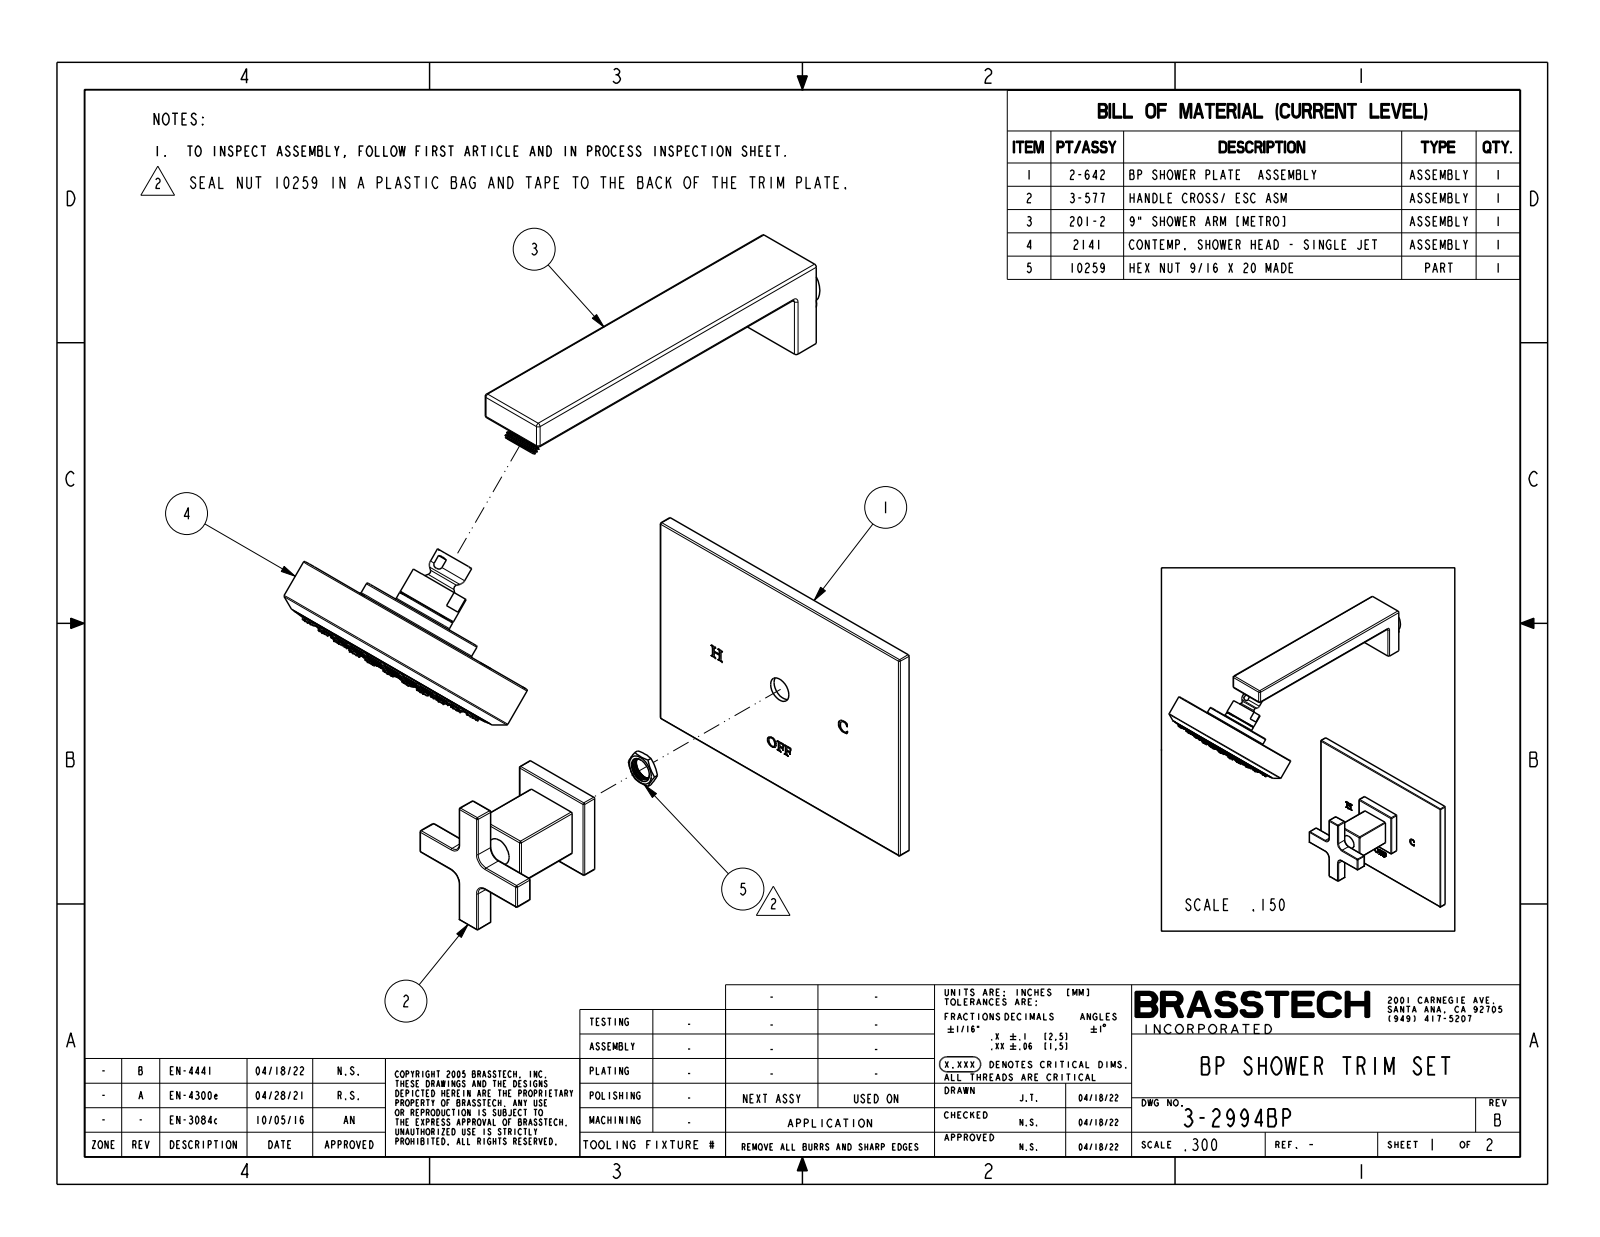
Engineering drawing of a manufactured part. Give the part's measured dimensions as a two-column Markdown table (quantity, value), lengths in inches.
| quantity | value |
| --- | --- |
| part name | 3-2994BP |
| STEP written by | CREO PARAMETRIC BY PTC INC, 2018400 (CONFIG_CONTROL_DESIGN) |
| units | inches |
| bodies | 2 solids, 1204 faces (183 planar, 272 cylindrical, 749 other) |
| overall size | 14.95 × 12.492 × 7.75 |
| volume | 65.66 in³ |
| surface area | 256.1 in² |
| round holes (diameter × count) | 0.05 × 90, 0.22 × 1, 5.256 × 1 |
| round bosses / shafts (diameter × count) | 1.4 × 2, 5.91 × 1, 5.22 × 1, 2.92 × 1, 0.905 × 1, 0.65 × 1, 0.523 × 1 |
| partial cylindrical surfaces (radius × count) | 0.03 × 48, 0.06 × 10, 0.25 × 4, 0.08 × 1, 0.475 × 1 |
| main face-to-face distances | 0.31, 0.654, 1.75, 0.291, 2.17, 3.33, 0.205, 1.545, 3.356, 3.046 |
| hole center spacings | 1.84, 2.27, 0.48, 0.952, 1.847, 0.944, 1.408, 1.84 |
